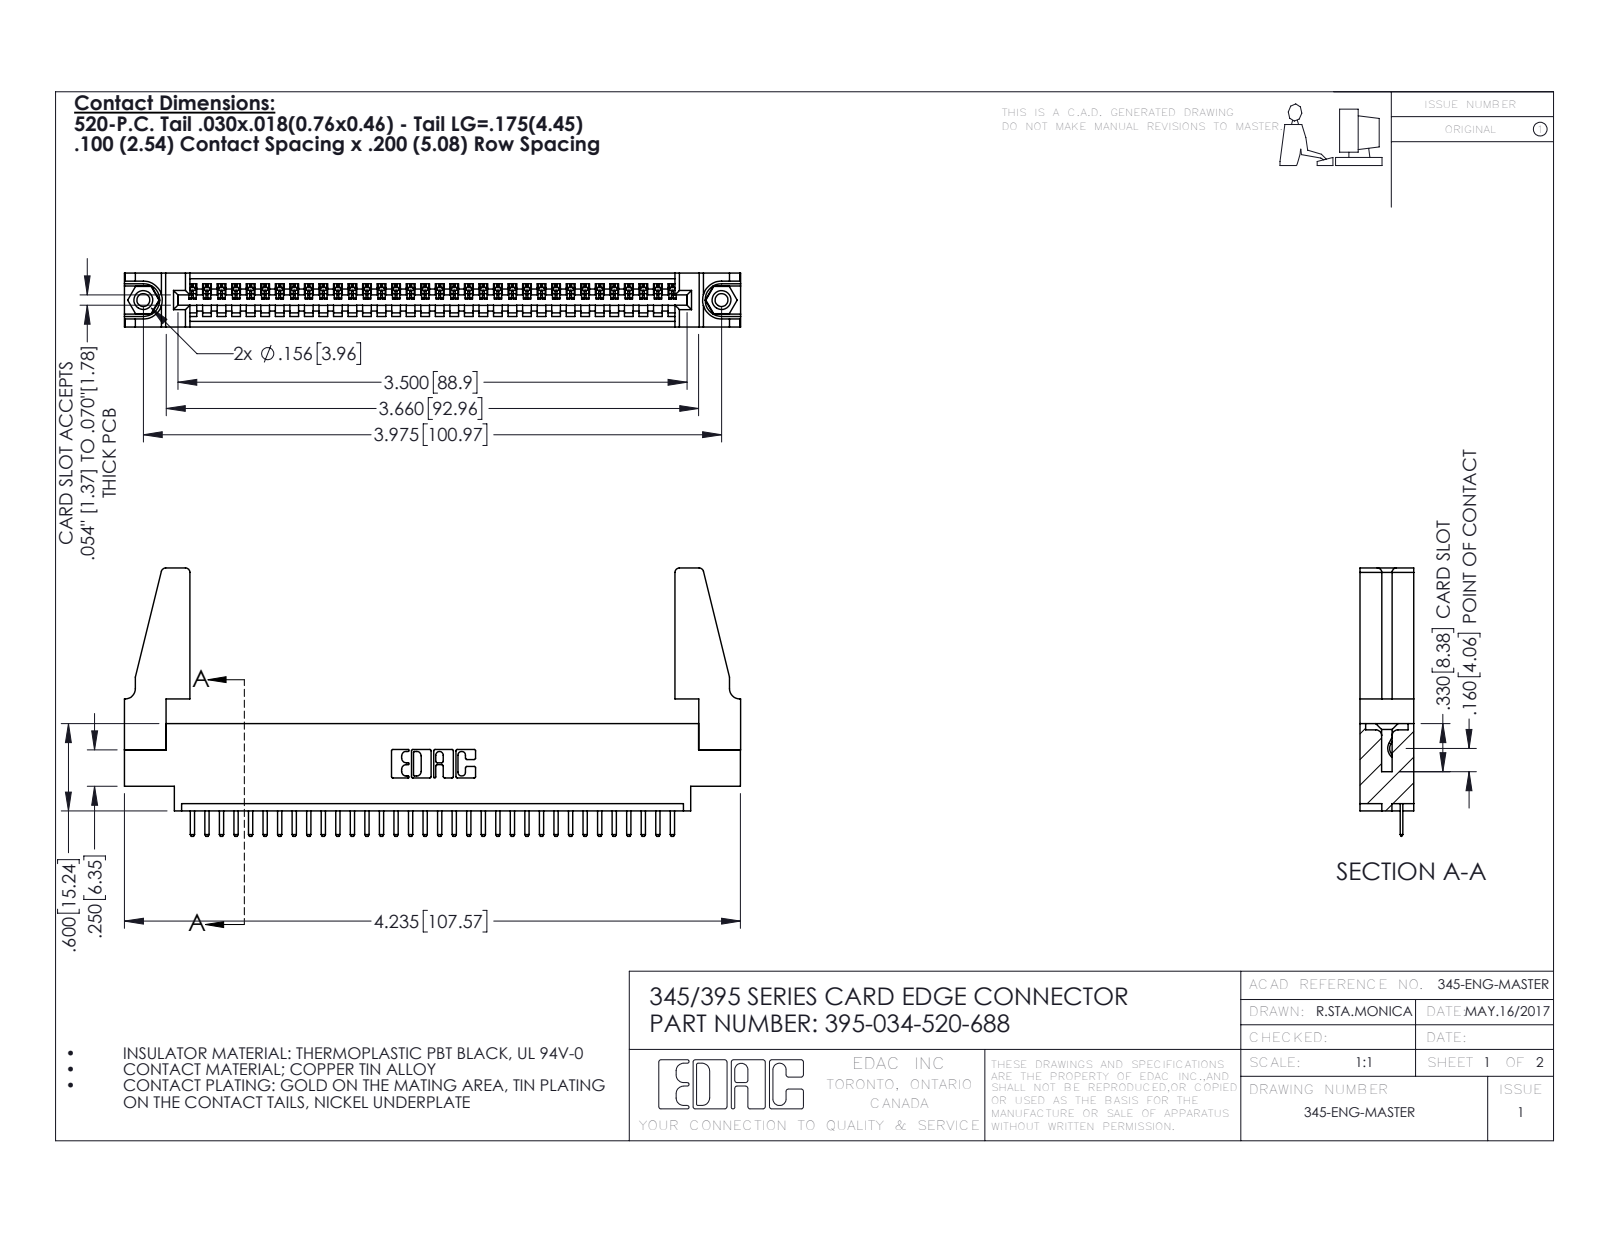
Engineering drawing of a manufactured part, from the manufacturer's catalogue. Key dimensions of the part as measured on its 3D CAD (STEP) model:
Part name (STEP PRODUCT): 345-220-078_345-220-088; 345 Part_0.170 Offset - 0.156 Dia-TH; 345-250-001_345-250-001-102; 345-292-001_345-293-120 (+1 more)
STEP written by: SolidWorks 2016 (CONFIG_CONTROL_DESIGN)
Units: inches
Bodies: 39 solids, 2362 faces (1584 planar, 762 cylindrical, 16 other)
Overall size (bounding box): 4.236 × 1.845 × 0.37
Volume: 0.805 in³ · Surface area: 24.86 in²
Round holes (diameter × count): ⌀0.089 ×2, ⌀0.125 ×2, ⌀0.156 ×2, ⌀0.064 ×1
Round bosses / shafts (diameter × count): ⌀0.155 ×2
Partial cylindrical surfaces — rounded edges, fillets, slot ends (radius × count): R0.01 ×70, R0.006 ×68, R0.01 ×22, R0.03 ×8, R0.007 ×6, R0.031 ×6, R0.026 ×3, R0.031 ×2
Main face-to-face distances: 0.37, 0.072, 0.298, 0.2, 0.098, 0.272, 0.025, 0.225, 0.072, 0.175
Hole centre spacings: 0.27, 3.74, 3.975
